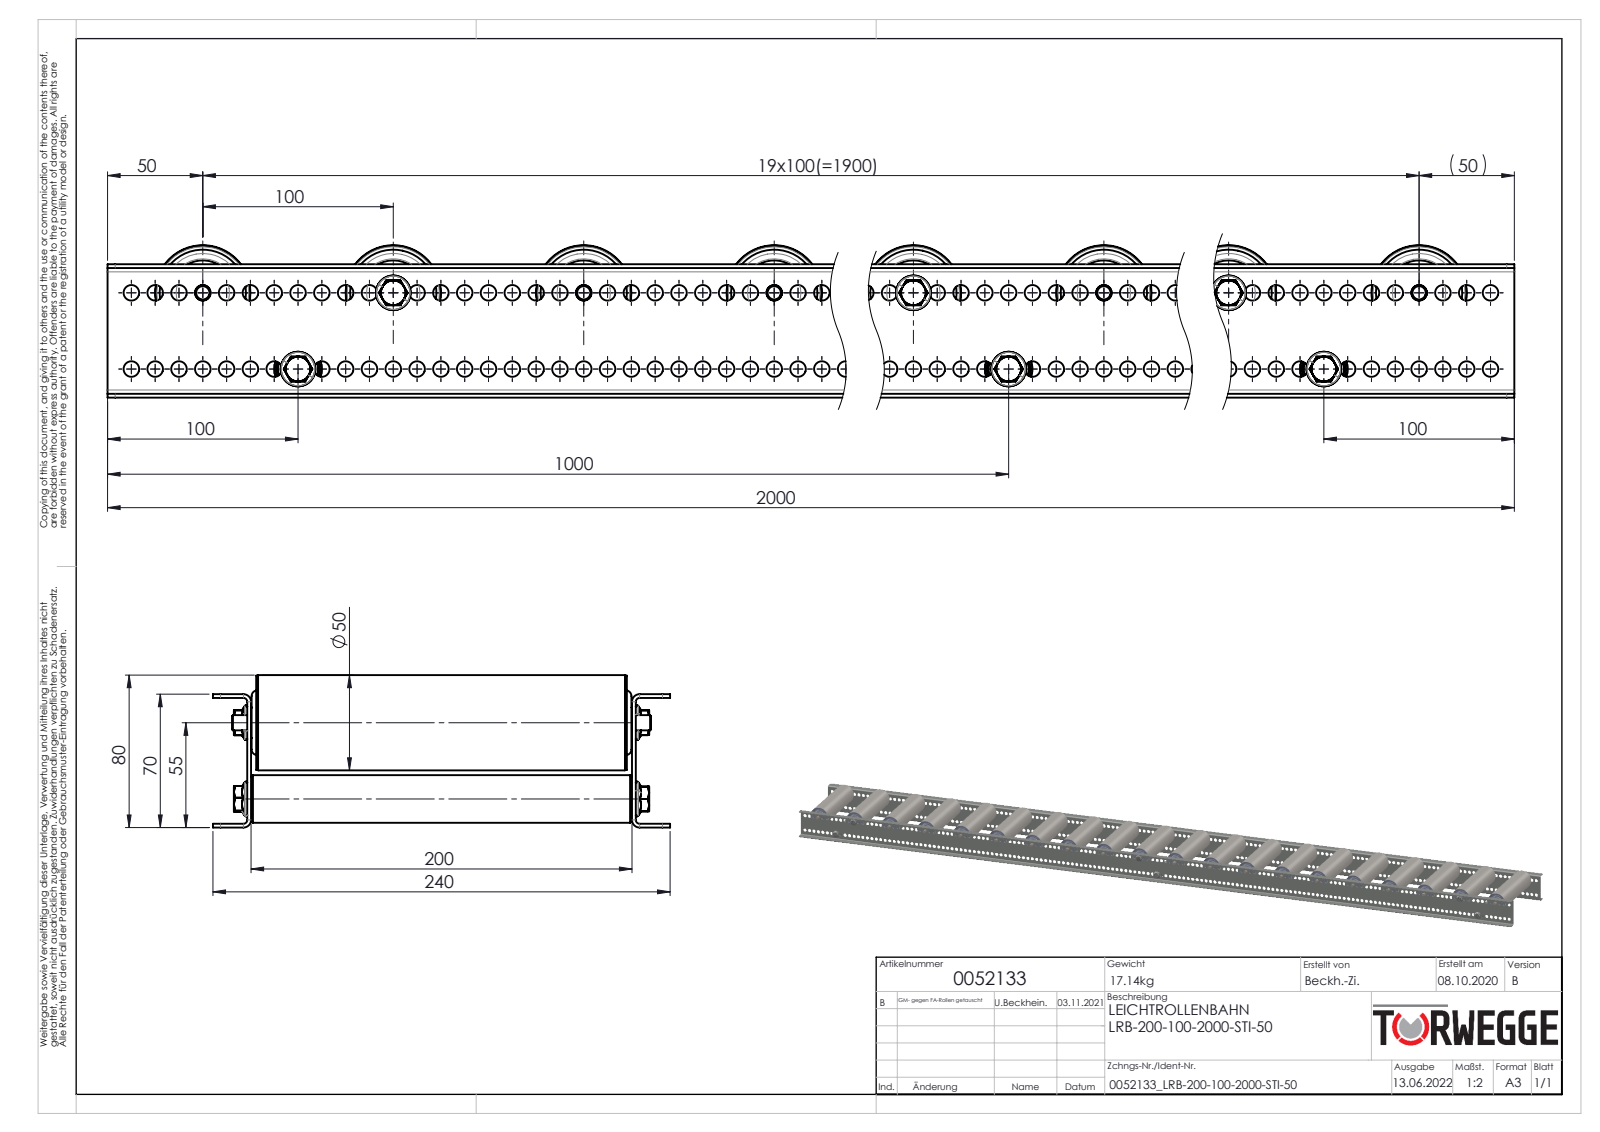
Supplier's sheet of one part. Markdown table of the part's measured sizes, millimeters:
| quantity | value |
| --- | --- |
| part name | 0039780-Achse-ST-Ø12-KFG_IGM8-AL=200-TRG; Traversen_KFG_L200; 0026295_Typ-TRG_50x1,5-8; Druckfeder_1,2x10x30 (+8 more) |
| STEP written by | SolidWorks 2020 (AUTOMOTIVE_DESIGN) |
| units | millimeters |
| bodies | 476 solids, 8806 faces (1716 planar, 3328 cylindrical, 3762 other) |
| overall size | 2000 × 240 × 80 |
| volume | 2 382 000 mm³ |
| surface area | 2 794 000 mm² |
| round holes (diameter × count) | 8.2 × 318, 17.1 × 20, 18.5 × 20, 27.7 × 20, 45.3 × 20, 47 × 20, 7.6 × 17, 6.8 × 6, 12 × 3, 12.2 × 3, 19.2 × 3, 21 × 3 |
| round bosses / shafts (diameter × count) | 8 × 23, 50 × 20, 49.5 × 20, 47.3 × 20, 29.7 × 20, 27.4 × 20, 27.3 × 20, 16 × 20 |
| partial cylindrical surfaces (radius × count) | 0.6 × 34, 0.75 × 34, 2.45 × 34, 4.87 × 17, 7 × 17, 2.5 × 12, 4 × 8, 2 × 4 |
| main face-to-face distances | 2, 202, 68, 200, 204, 70, 66, 1, 2.3, 201.7 |
| hole center spacings | 12.5, 25, 37.5, 50, 62.5, 75, 87.5, 100 |
